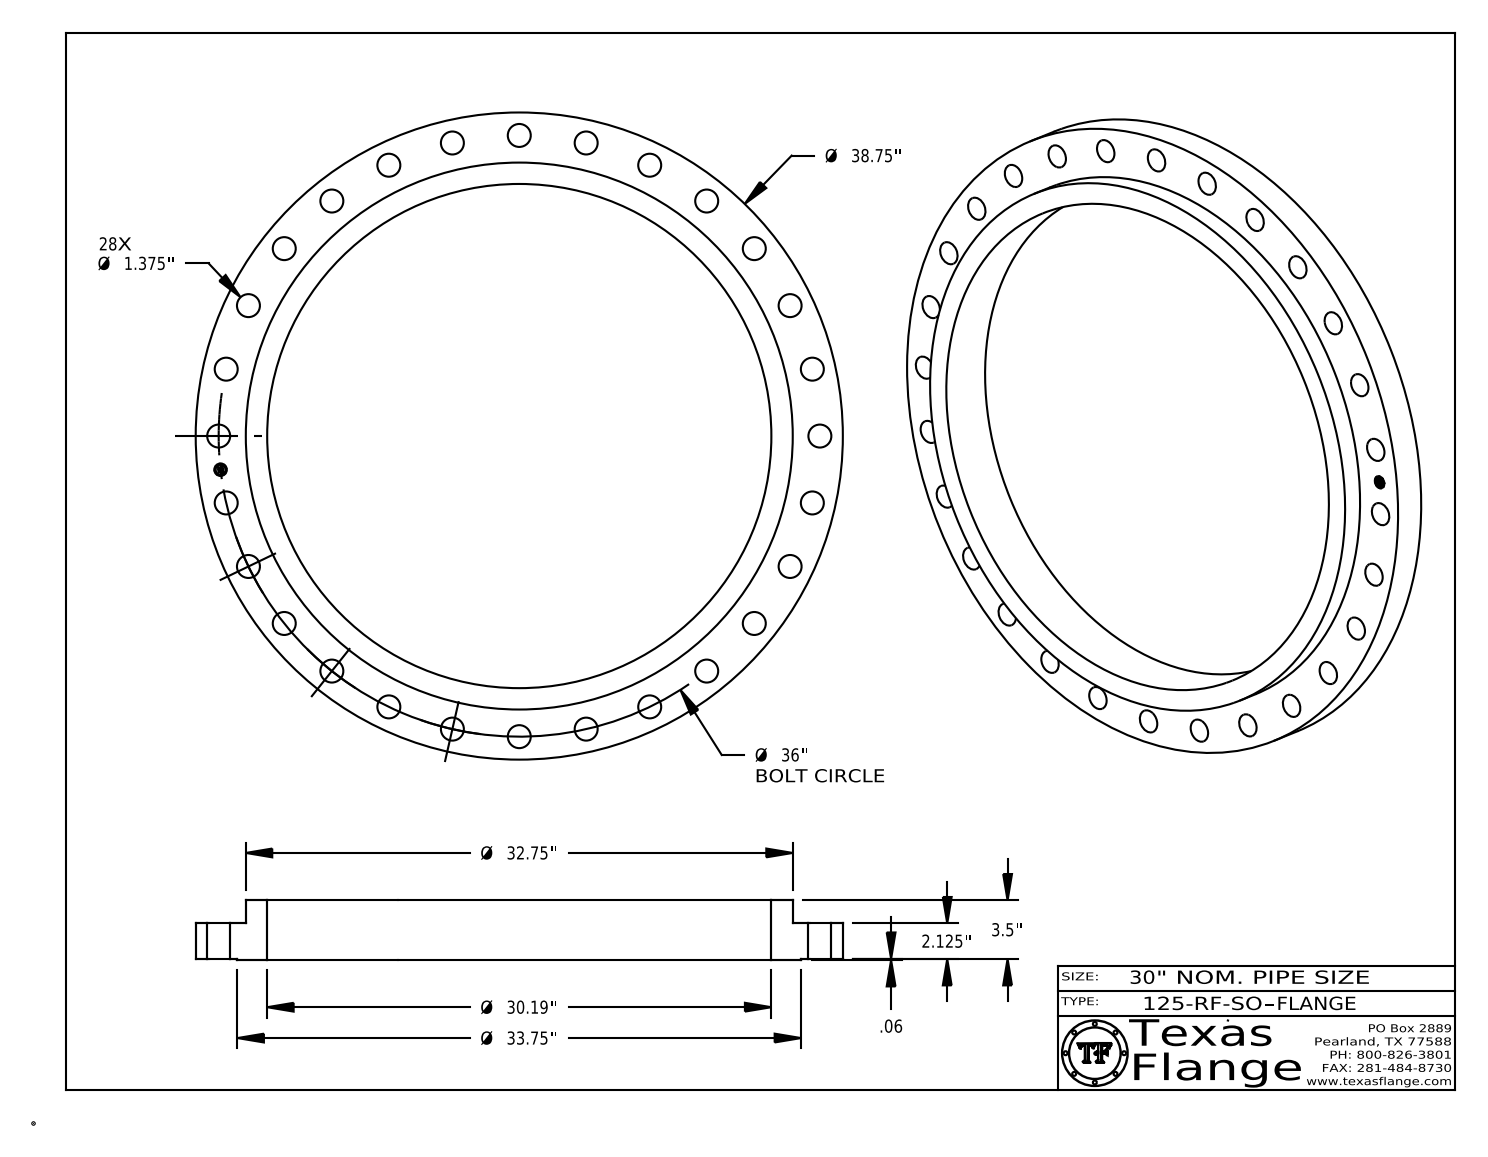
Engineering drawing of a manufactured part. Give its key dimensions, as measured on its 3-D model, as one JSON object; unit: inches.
{"part_name": "125-RF-SO-B16.1", "step_written_by": "CATIA V5 STEP AP214 (AUTOMOTIVE_DESIGN)", "units": "inches", "bodies": {"solids": 1, "faces": 453, "planar": 369, "cylindrical": 84, "other": 0}, "overall_size": [38.75, 38.75, 3.563], "volume_in3": 1082, "surface_area_in2": 1846, "round_holes": [[1.375, 28], [0.75, 1], [30.19, 1]], "round_bosses_or_shafts": [[0.045, 8], [38.75, 1], [33.75, 1], [32.75, 1], [0.591, 1]], "face_to_face_distances": [2.125, 0.063, 2.188, 3.563, 3.5, 1.375, 2.172, 2.11, 0.015, 1.39], "hole_center_spacings": [18, 19.153, 4.031, 8.011, 11.89, 15.62, 22.446, 25.456]}
